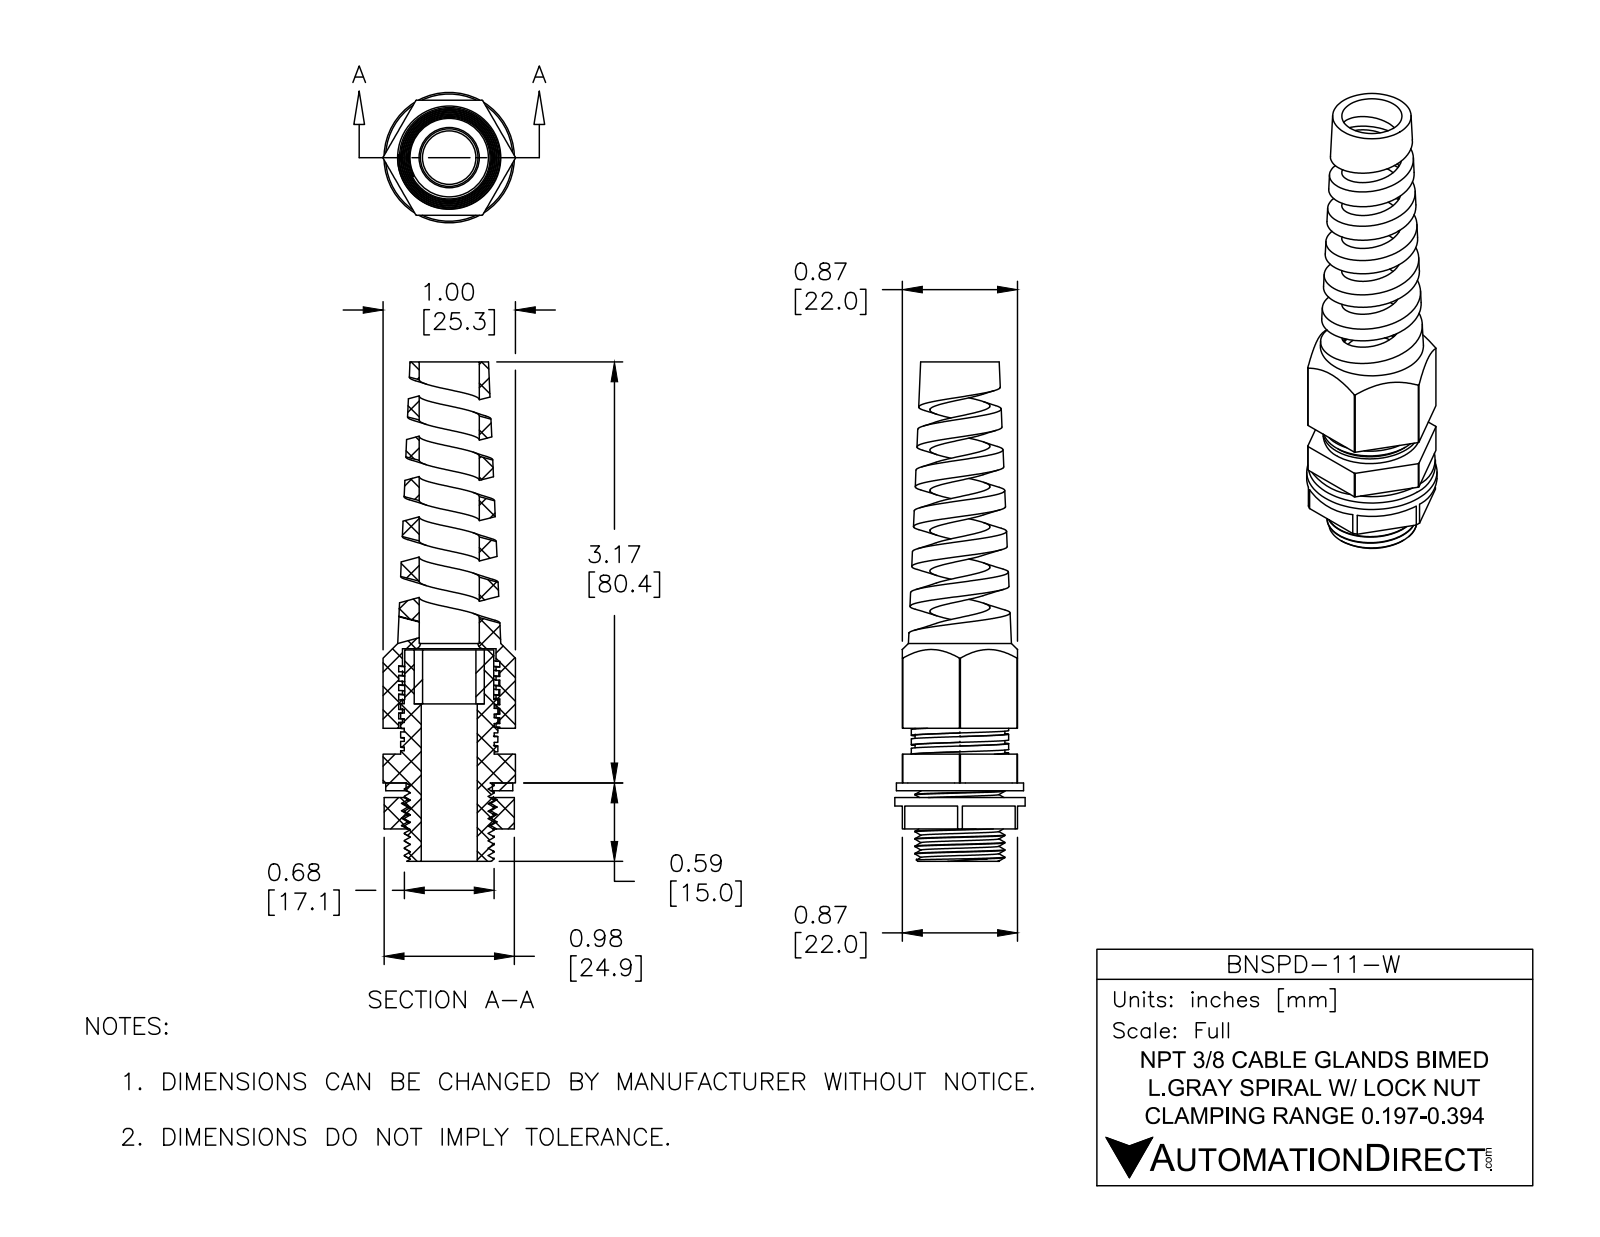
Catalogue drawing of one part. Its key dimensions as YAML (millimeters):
part_name: "BNSPAX-11-W"
step_written_by: "SolidWorks 2015 (CONFIG_CONTROL_DESIGN)"
units: millimeters
bodies: {solids: 5, faces: 241, planar: 104, cylindrical: 103, other: 34}
overall_size: [95.43, 25.3, 24.9]
volume: 14512
surface_area: 16461
round_holes:
  - {diameter: 10.2, count: 1}
  - {diameter: 10.72, count: 1}
  - {diameter: 11.5, count: 1}
  - {diameter: 13.4, count: 1}
  - {diameter: 16.02, count: 1}
  - {diameter: 16.5, count: 1}
  - {diameter: 17.9, count: 1}
round_bosses_or_shafts:
  - {diameter: 24.9, count: 1}
  - {diameter: 24.3, count: 1}
  - {diameter: 18.6, count: 1}
  - {diameter: 17.14, count: 1}
  - {diameter: 17, count: 1}
partial_cylinders:
  - {radius: 12.65, count: 1}
face_to_face_distances: [22, 2.8, 1.3, 1.5, 6, 7.3, 8.8, 0.5, 14.3, 8.3]
